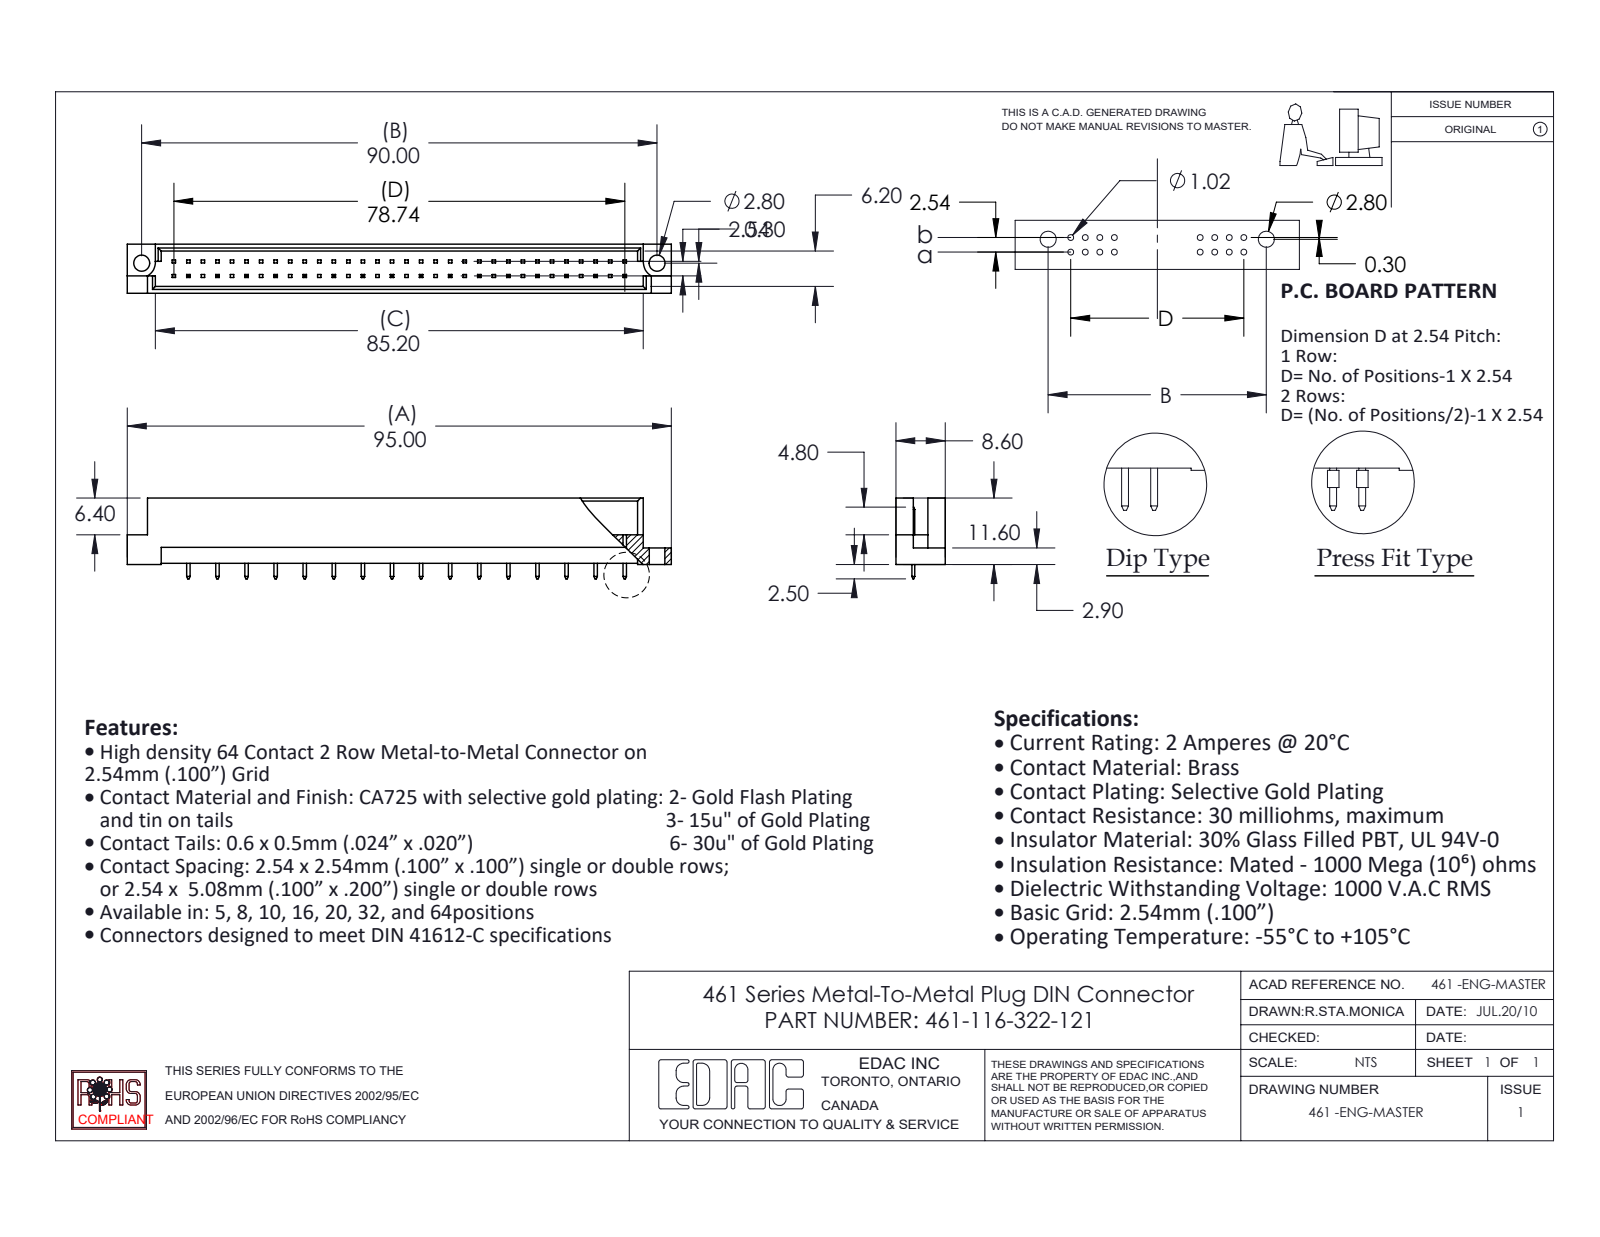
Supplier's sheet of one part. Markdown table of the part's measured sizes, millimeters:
| quantity | value |
| --- | --- |
| part name | 461 Part_64; 461-290_22; 461-116-322-221 |
| STEP written by | SolidWorks 2020 (CONFIG_CONTROL_DESIGN) |
| units | millimeters |
| bodies | 17 solids, 529 faces (522 planar, 7 cylindrical, 0 other) |
| overall size | 95 × 14.1 × 8.6 |
| volume | 4 715 mm³ |
| surface area | 6 106 mm² |
| round holes (diameter × count) | 2.8 × 2 |
| partial cylindrical surfaces (radius × count) | 2.8 × 2 |
| main face-to-face distances | 1.2, 7.4, 8.6, 6.2, 5, 3.28, 5.32, 2.08, 4.12, 2.78 |
| hole center spacings | 90 |
